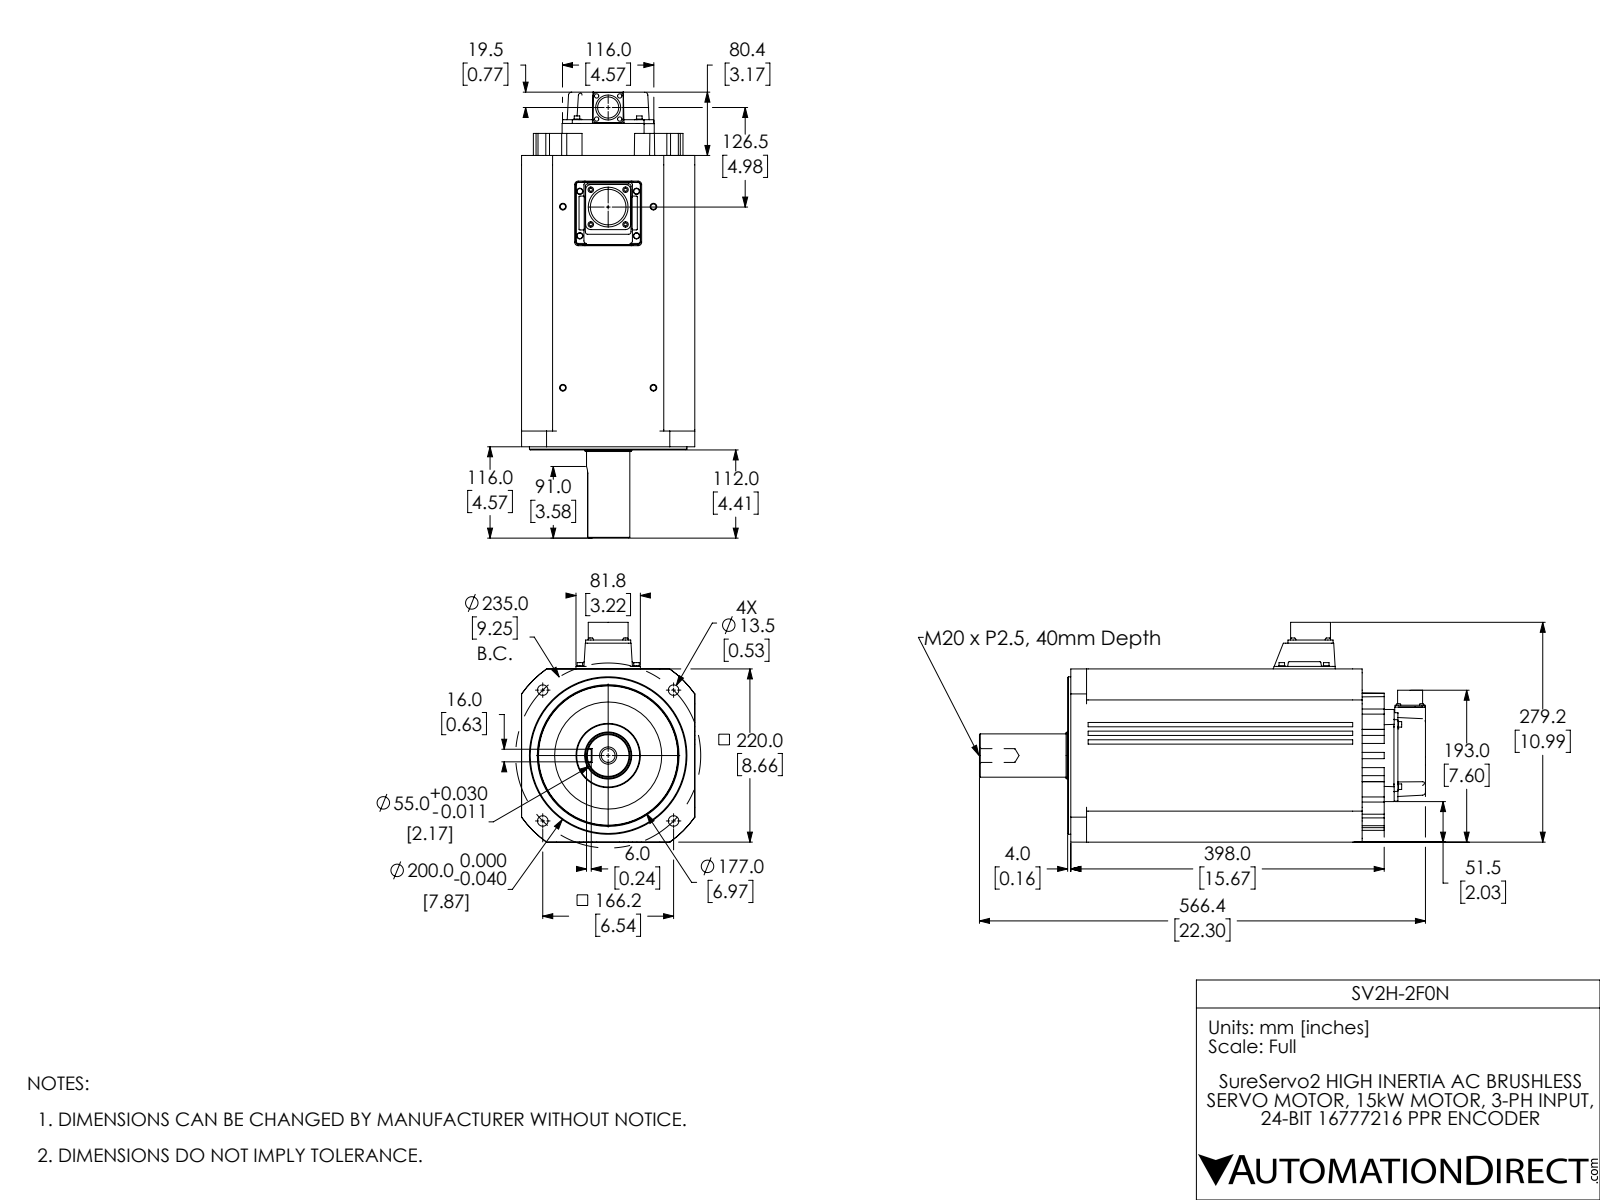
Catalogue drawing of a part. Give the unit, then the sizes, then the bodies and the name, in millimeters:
Units: millimetres
Overall size (bounding box): 566.5 × 279.2 × 220
Round holes (diameter × count): ⌀4.3 ×4, ⌀4.6 ×4, ⌀6.8 ×4, ⌀13.5 ×4, ⌀17.5 ×1, ⌀26.9 ×1, ⌀45.3 ×1, ⌀180 ×1
Round bosses / shafts (diameter × count): ⌀8 ×8, ⌀7 ×8, ⌀4 ×4, ⌀200 ×1, ⌀178 ×1, ⌀136 ×1, ⌀59.8 ×1, ⌀55 ×1
Partial cylindrical surfaces — rounded edges, fillets, slot ends (radius × count): R0.5 ×21, R5 ×20, R3 ×14, R4 ×8, R1 ×4, R4.5 ×4, R6 ×4, R6.6 ×4
Main face-to-face distances: 220, 39.4, 180.6, 5.5, 141.2, 11, 4, 16.5, 8, 374
Hole centre spacings: 117.5, 166.2, 29, 41.2, 42.8, 51.3, 56.5, 57.5
Volume: 17 030 000 mm³ · Surface area: 582 300 mm²
Bodies: 1 solid, 734 faces (325 planar, 204 cylindrical, 205 other)
Part name (STEP PRODUCT): SV2H-2F0N EXT 1c
STEP written by: SolidWorks 2017 (AUTOMOTIVE_DESIGN)
